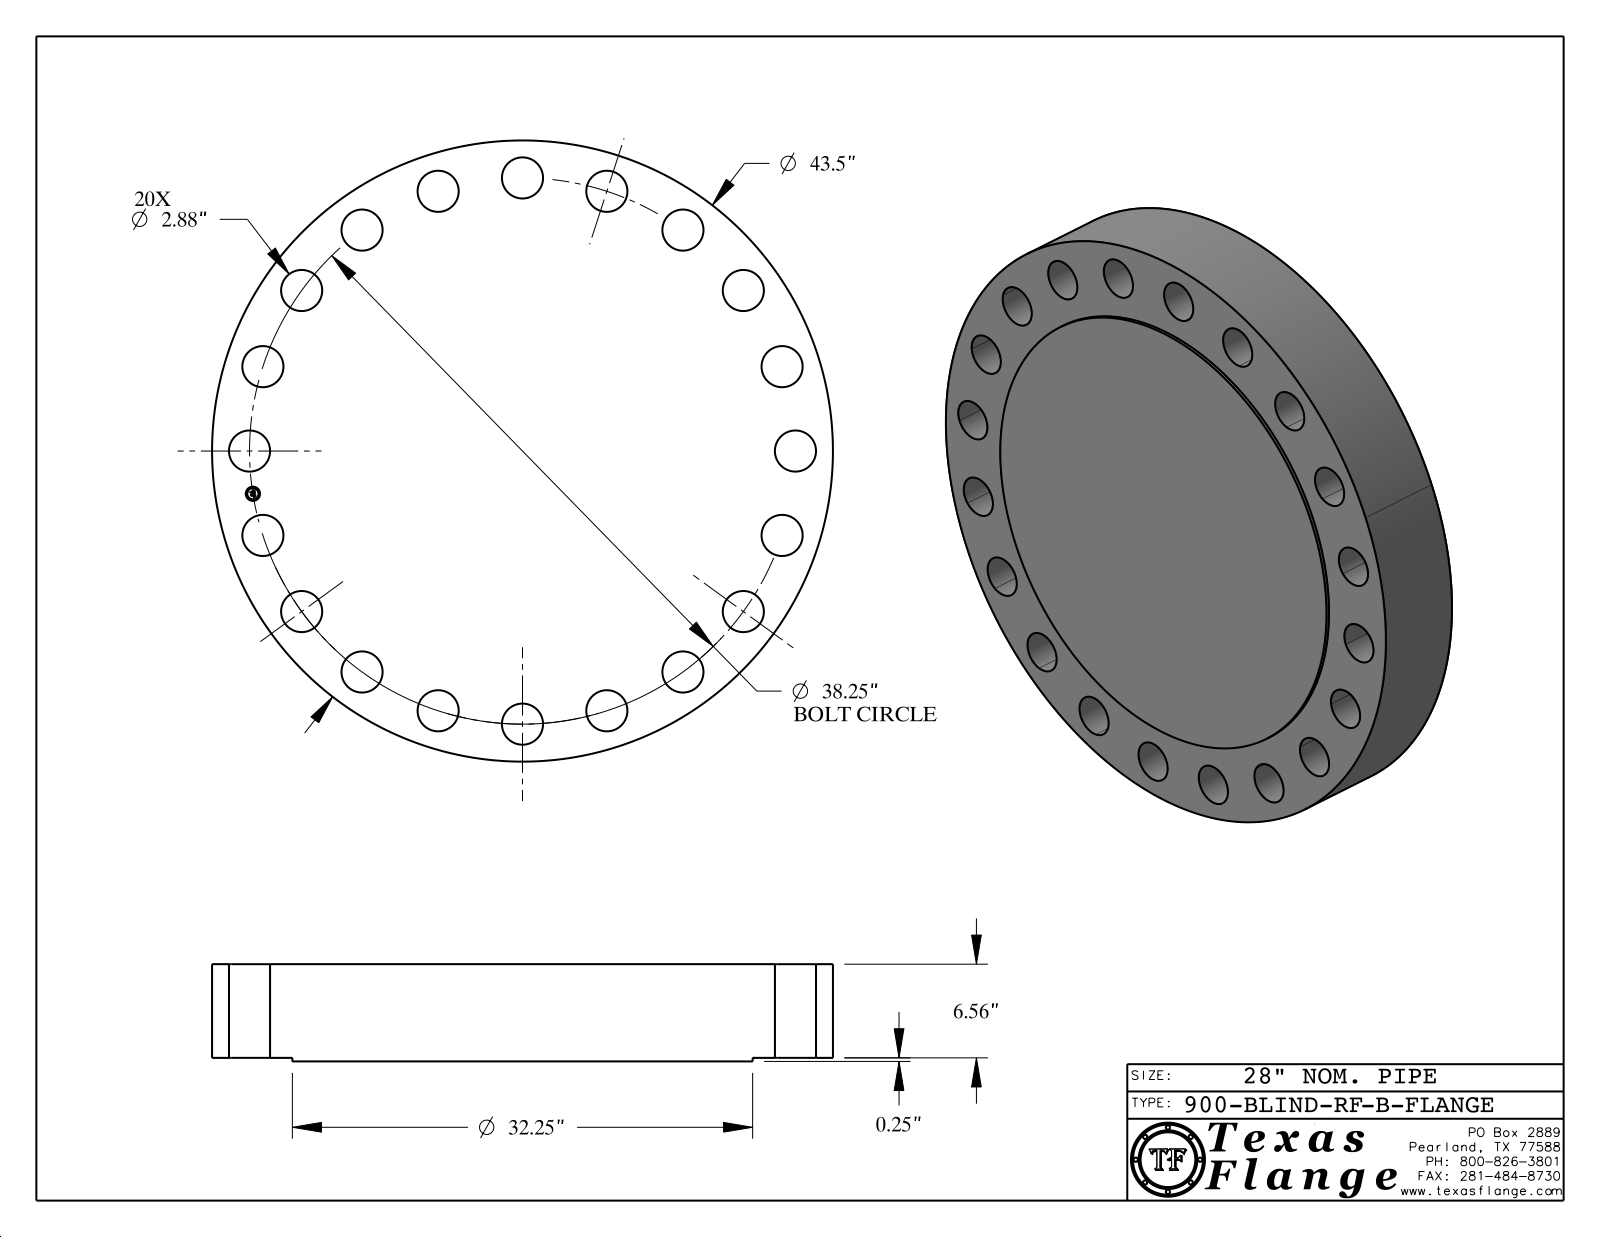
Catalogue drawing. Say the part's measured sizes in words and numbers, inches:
The part is named "900-BLIND-RF, Series B". Its 3-D file was written by "CATIA V5 STEP AP214 (AUTOMOTIVE_DESIGN)". It is 1 solid with 432 faces: 368 planar, 64 cylindrical and 0 other. Overall it measures 43.5 by 43.5 by 6.81 inches. Its volume is 9 099 cubic inches and its surface area 4 821 square inches. Round holes: 20 of diameter 2.88, 1 of diameter 1. Round bosses or shafts: 8 of diameter 0.061, 1 of diameter 43.5, 1 of diameter 32.25, 1 of diameter 0.788. The main face-to-face distances are 6.81, 0.25, 6.56, 6.795, 6.545, 0.015, 0.298, 0.293, 0.019, 0.054. The hole center spacings are 30.945, 36.378, 37.779, 11.82, 27.047, 34.081, 5.984, 17.365.
